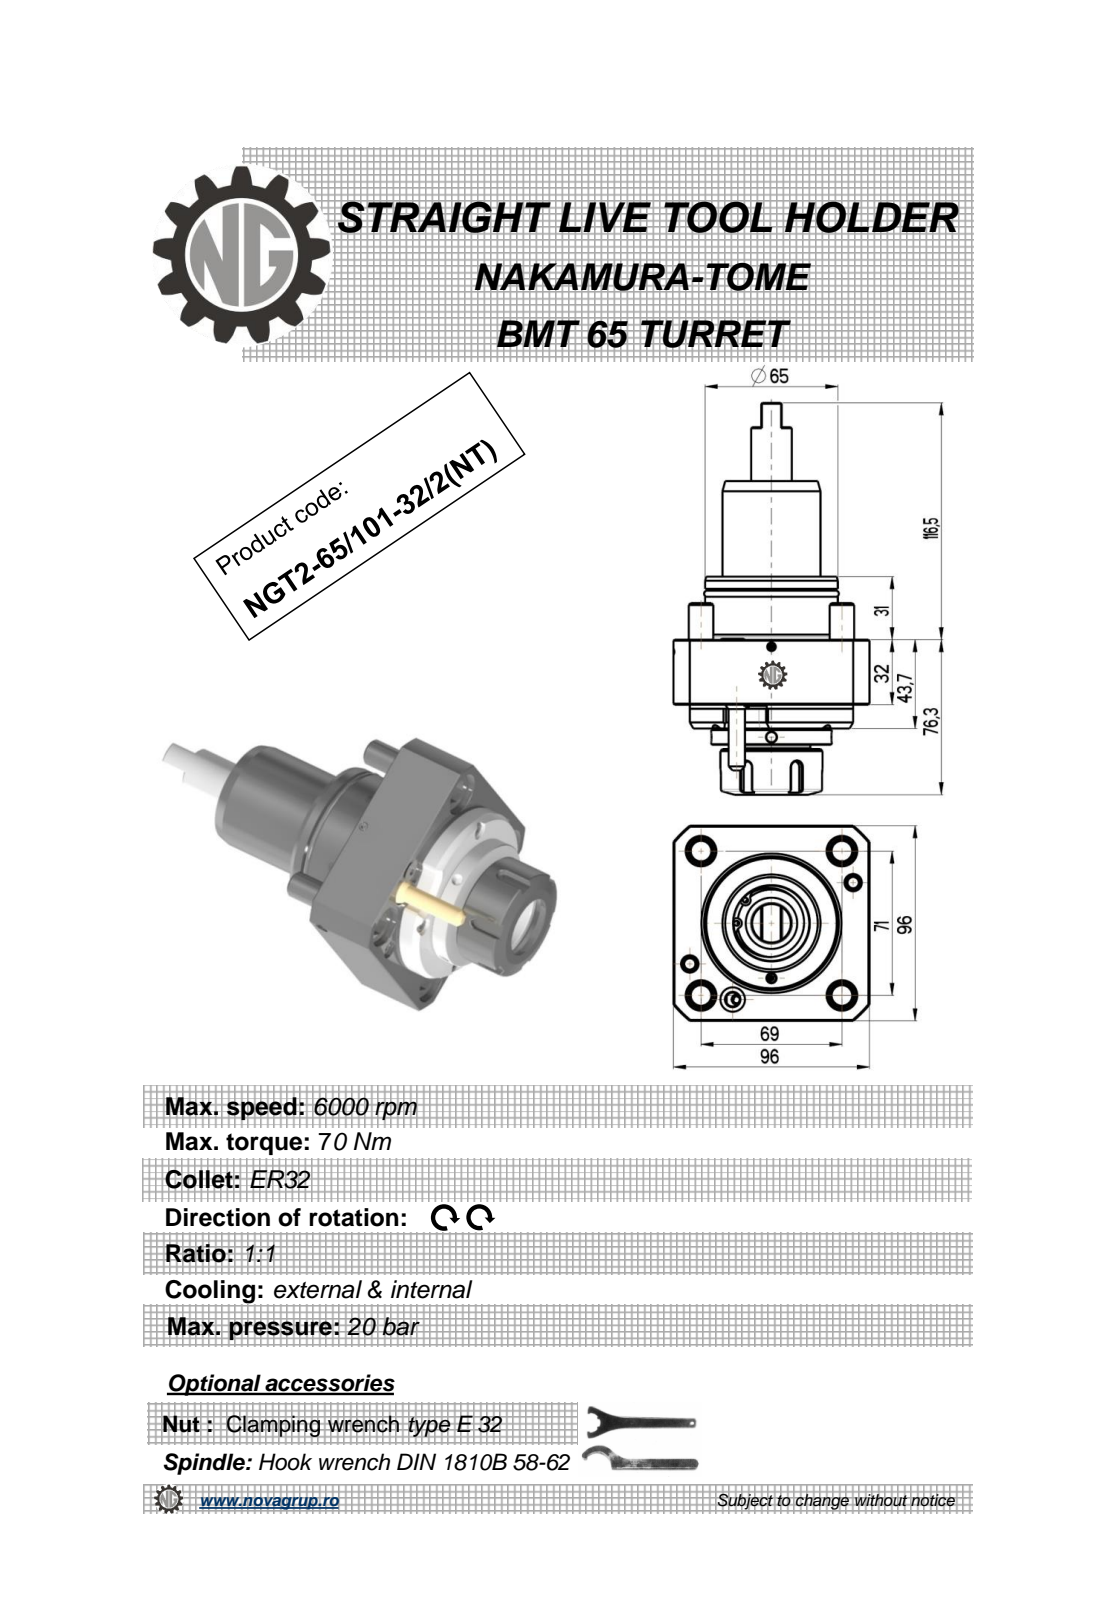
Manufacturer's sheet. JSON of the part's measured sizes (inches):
{"part_name": "NGT2_65_101_32_1_NT", "step_written_by": "PRO/ENGINEER BY PARAMETRIC TECHNOLOGY CORPORATION, 2010280 (CONFIG_CONTROL_DESIGN)", "units": "inches", "bodies": {"solids": 2, "faces": 238, "planar": 80, "cylindrical": 68, "other": 90}, "overall_size": [7.591, 3.78, 3.78], "volume_in3": 37.66, "surface_area_in2": 99.84, "round_holes": [[0.197, 3], [0.118, 1], [0.268, 1], [1.063, 1]], "round_bosses_or_shafts": [[0.472, 4], [3.15, 1], [2.559, 1], [2.362, 1], [2.323, 1], [1.969, 1], [1.89, 1], [1.811, 1]], "partial_cylinders_radius": [[0.009, 6], [0.118, 5], [0.236, 4], [0.031, 2], [2.461, 1]], "face_to_face_distances": [3.78, 1.26, 1.72, 0.461, 1.22, 2.48, 2.941, 3.256, 2.035, 0.776], "hole_center_spacings": [0.079, 1.621, 1.655]}
